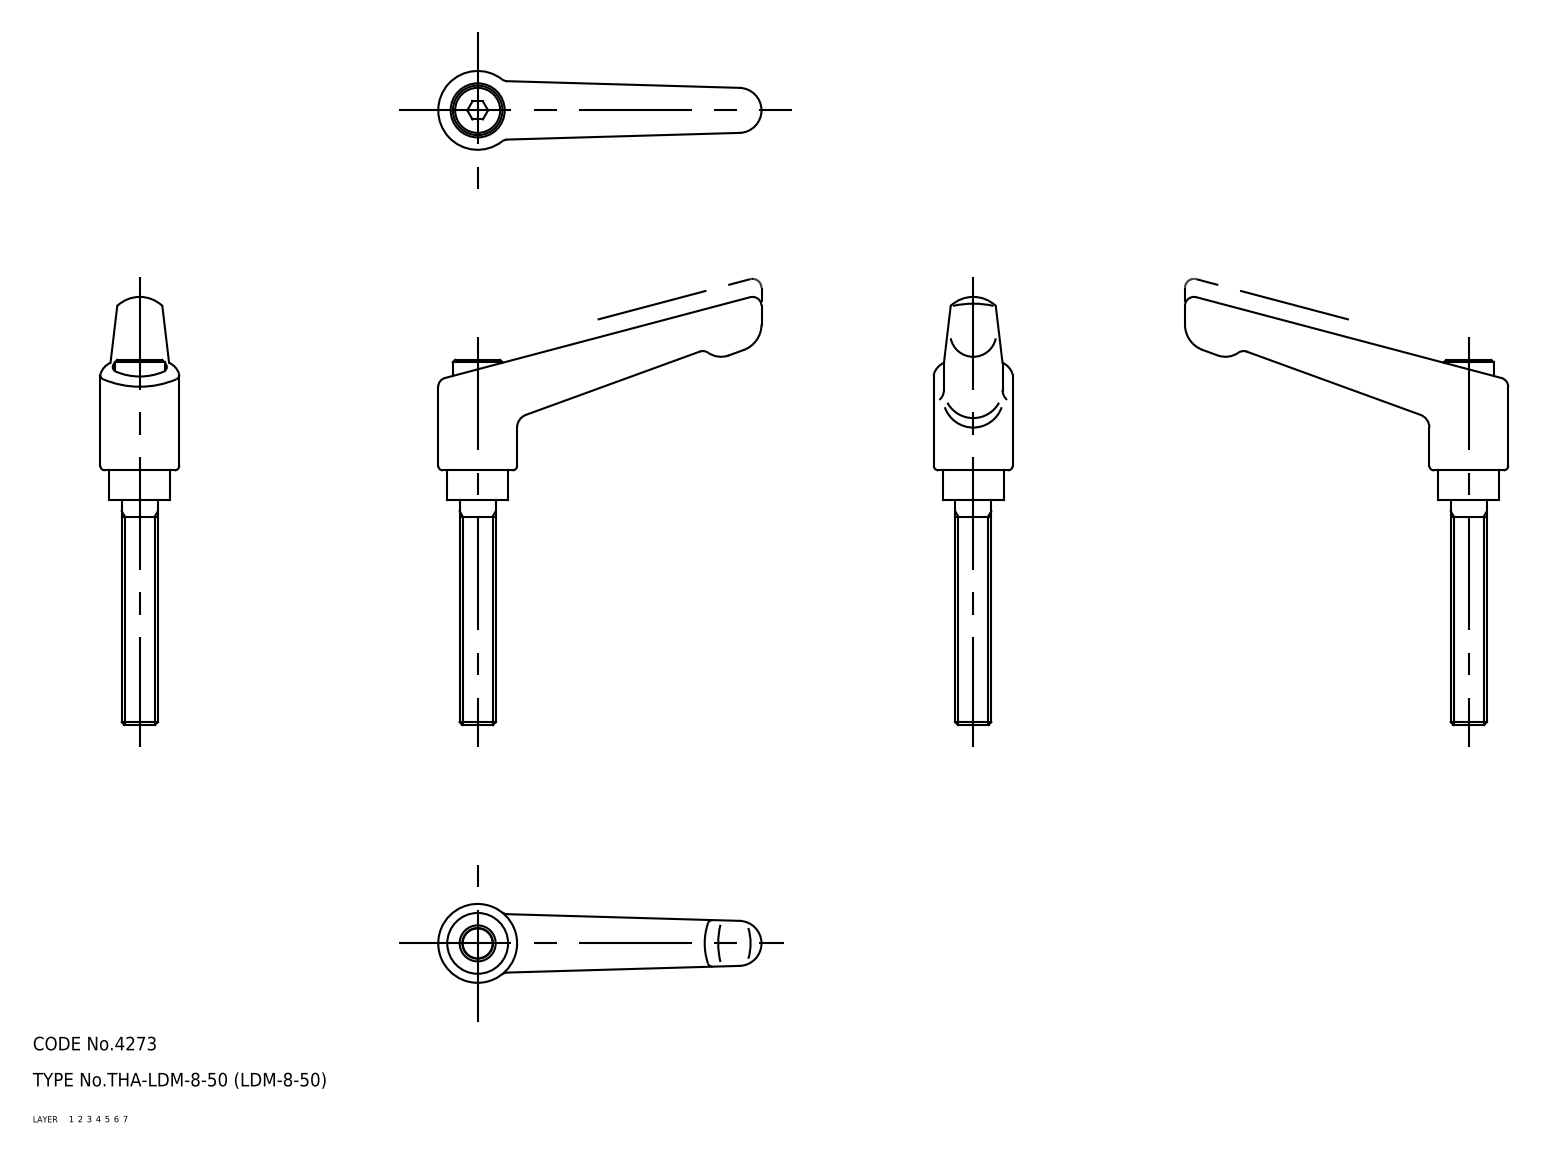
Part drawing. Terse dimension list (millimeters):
name: sleeve; screw; handle; LDM_8_50_26545_36
written by: CADfix (AUTOMOTIVE_DESIGN)
unit: mm
bodies: 3 solids, 75 faces (0 planar, 0 cylindrical, 75 other)
size: 95 × 71.75 × 17.5
volume: 14 626 mm³; area: 7 272 mm²
